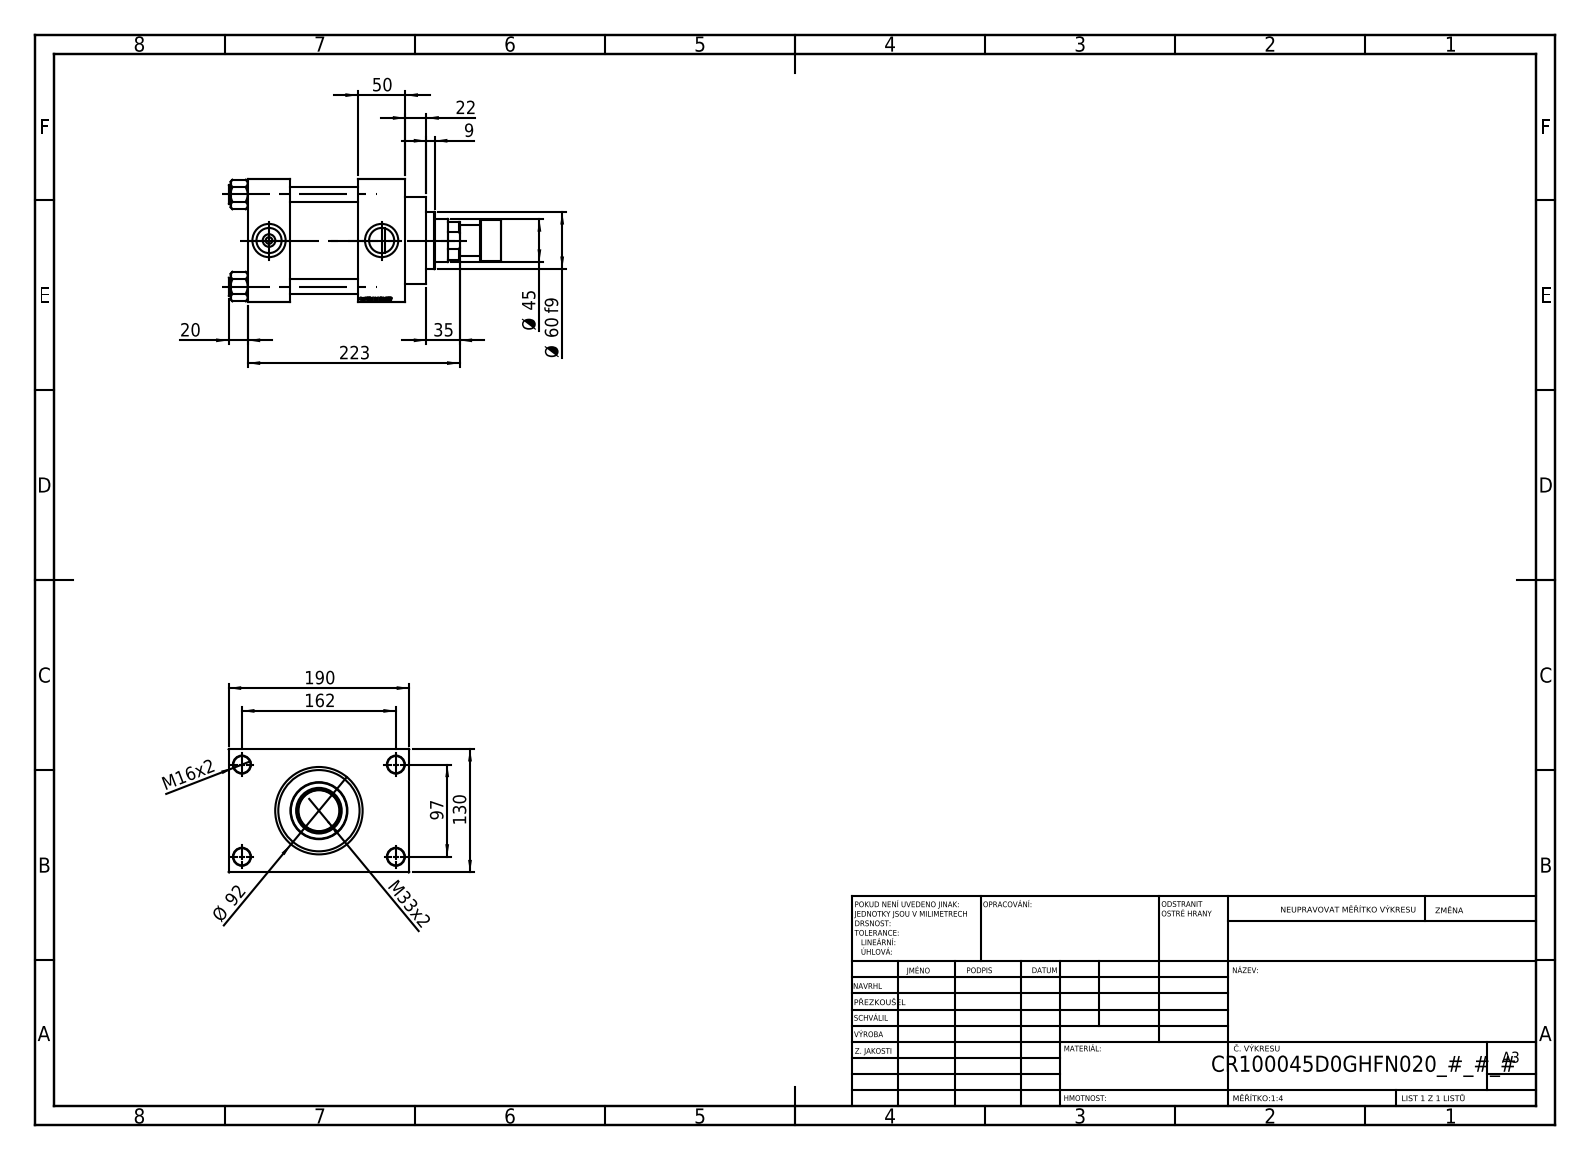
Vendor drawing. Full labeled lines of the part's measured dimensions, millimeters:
Part name (STEP PRODUCT): NUT_M5_D; V215_VC_A; V215CR_D_Body; V215CR_D_TYCINKA (+2 more)
STEP written by: SolidWorks 2019 (CONFIG_CONTROL_DESIGN)
Units: millimetres
Bodies: 12 solids, 1164 faces (548 planar, 92 cylindrical, 524 other)
Overall size (bounding box): 287 × 190 × 130
Volume: 2 643 000 mm³ · Surface area: 363 256 mm²
Round holes (diameter × count): ⌀16 ×4, ⌀18 ×4, ⌀7 ×2, ⌀26.44 ×2, ⌀35 ×2, ⌀31.5 ×1, ⌀45 ×1, ⌀48 ×1, ⌀76 ×1, ⌀85.5 ×1, ⌀100 ×1
Round bosses / shafts (diameter × count): ⌀19 ×4, ⌀106 ×1, ⌀92 ×1, ⌀60 ×1, ⌀44 ×1, ⌀33 ×1
Main face-to-face distances: 130, 116, 45, 71, 166, 121, 50, 30, 160, 70
Hole centre spacings: 32.55, 68.52, 94.41, 96.9, 102.27, 129.45, 161.73, 97
